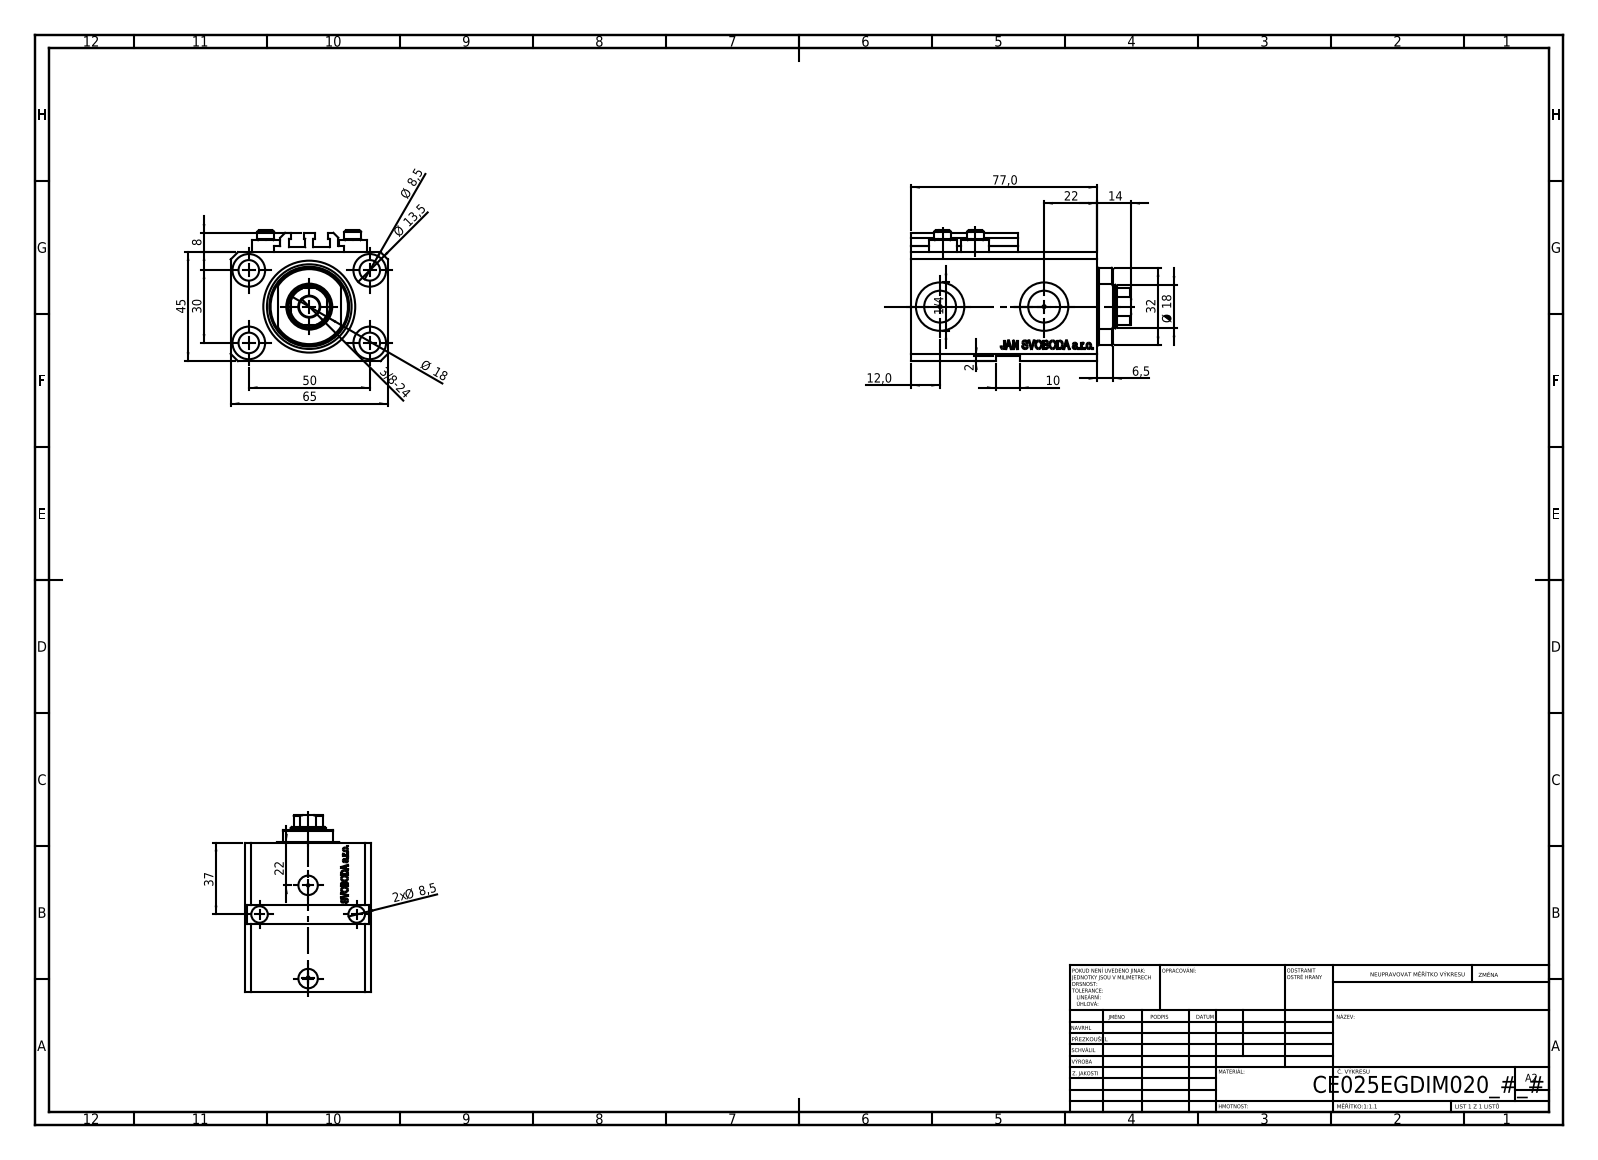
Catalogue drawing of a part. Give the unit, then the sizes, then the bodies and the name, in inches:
Units: inches
Overall size (bounding box): 3.583 × 2.559 × 2.126
Round holes (diameter × count): ⌀0.335 ×7, ⌀0.049 ×4, ⌀0.157 ×4, ⌀0.531 ×4, ⌀0.394 ×2, ⌀0.518 ×2, ⌀0.787 ×2, ⌀0.709 ×1, ⌀0.984 ×1, ⌀1.496 ×1
Round bosses / shafts (diameter × count): ⌀0.457 ×4, ⌀0.276 ×4
Partial cylindrical surfaces — rounded edges, fillets, slot ends (radius × count): R0.008 ×10, R0.335 ×1, R0.63 ×1
Main face-to-face distances: 1.772, 2.559, 2.48, 0.551, 3.031, 0.079, 0.272, 2.209, 2.76, 1.85
Hole centre spacings: 1.148, 1.969, 0.535, 0.595, 0.741, 0.747, 1.032, 1.048
Volume: 11.97 in³ · Surface area: 93.5 in²
Bodies: 8 solids, 1083 faces (515 planar, 138 cylindrical, 430 other)
Part name (STEP PRODUCT): V250CE_C_VCP; V250CE_VC_E; ALLEN BOLT V250CE; V250CE_E_Body
STEP written by: SolidWorks 2019 (CONFIG_CONTROL_DESIGN)
